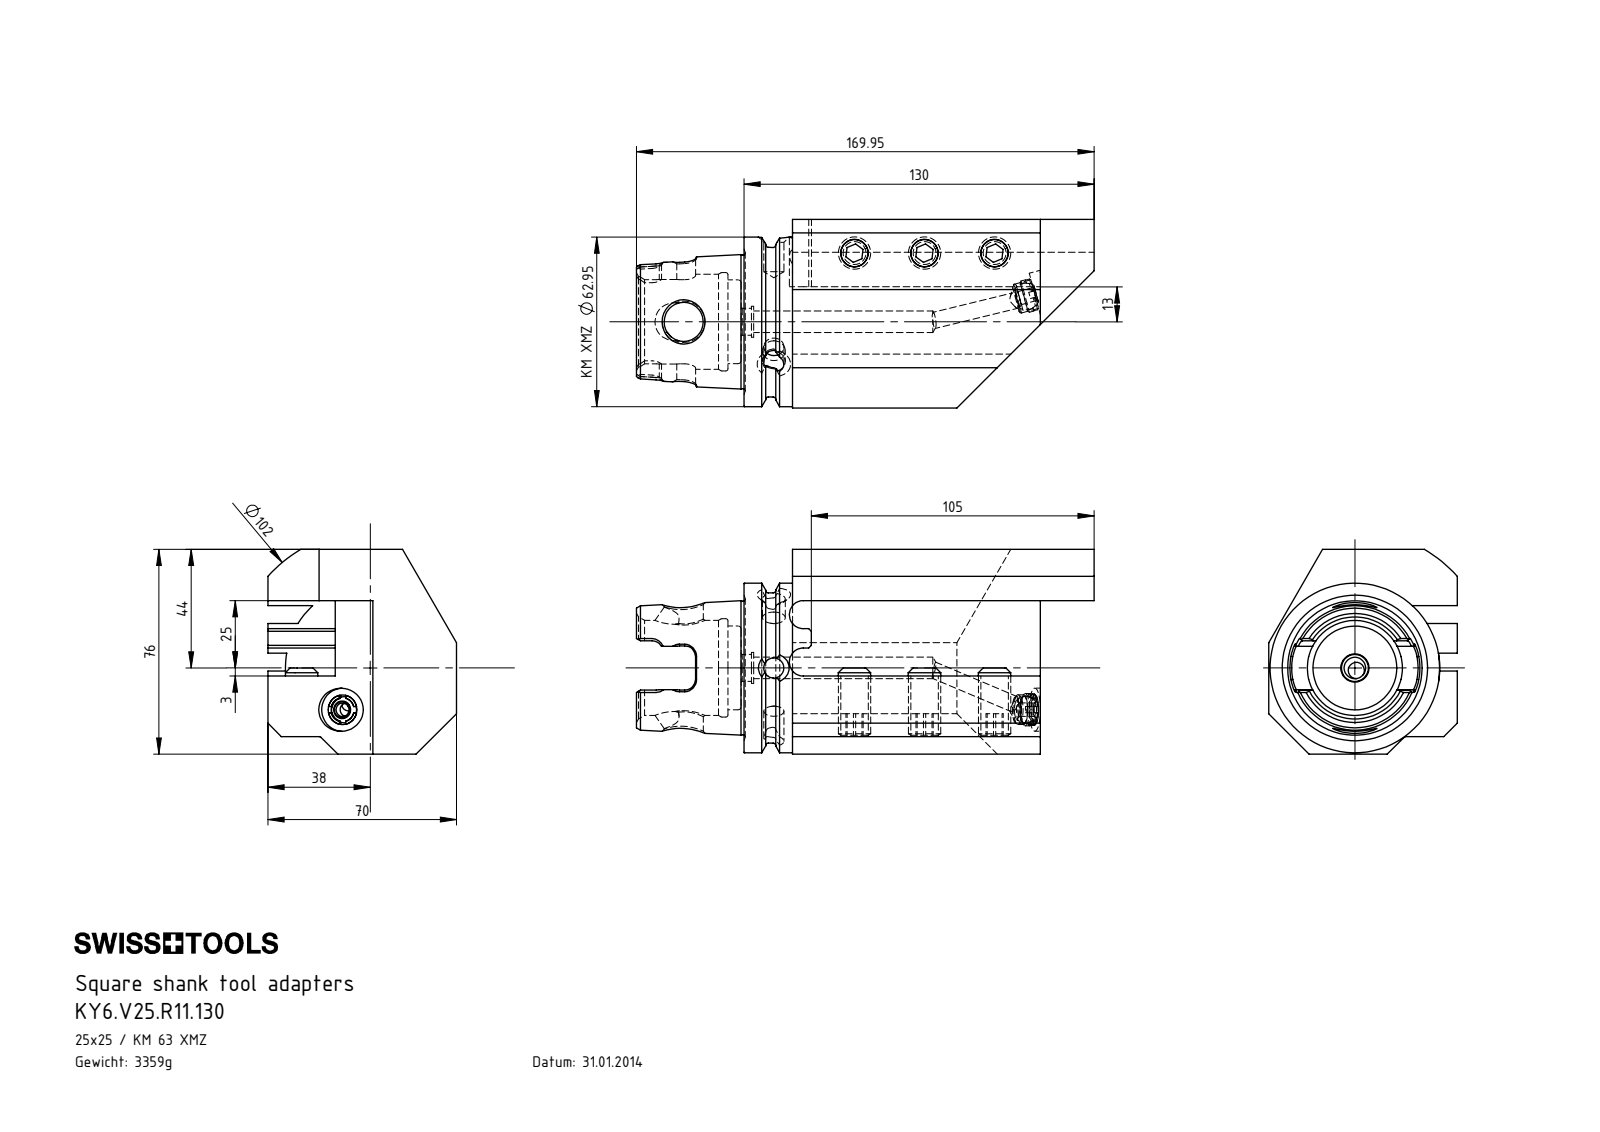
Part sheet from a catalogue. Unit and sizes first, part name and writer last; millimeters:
Units: millimetres
Overall size (bounding box): 169.95 × 76 × 70
Round holes (diameter × count): ⌀10.2 ×3, ⌀7.47 ×2, ⌀10 ×2, ⌀5 ×1, ⌀6 ×1, ⌀8 ×1, ⌀8.47 ×1, ⌀11 ×1, ⌀11.5 ×1, ⌀14.5 ×1, ⌀16 ×1, ⌀31.1 ×1
Round bosses / shafts (diameter × count): ⌀12 ×4, ⌀62.95 ×1, ⌀55.7 ×1
Partial cylindrical surfaces — rounded edges, fillets, slot ends (radius × count): R4 ×6, R5.2 ×2, R7.04 ×2, R4.4 ×1, R51 ×1
Main face-to-face distances: 25, 19, 57, 76, 29, 28, 47, 45, 70, 92
Hole centre spacings: 26, 52, 68.34, 92.97, 118.18
Volume: 434 259 mm³ · Surface area: 60 306 mm²
Bodies: 6 solids, 284 faces (97 planar, 76 cylindrical, 111 other)
Part name (STEP PRODUCT): KY6.V25.R11.130; KU1-U12.002.010; KU1-U12.002.010_A; KU1-U12.003.010_A (+2 more)
STEP written by: SolidWorks 2012 (CONFIG_CONTROL_DESIGN)
